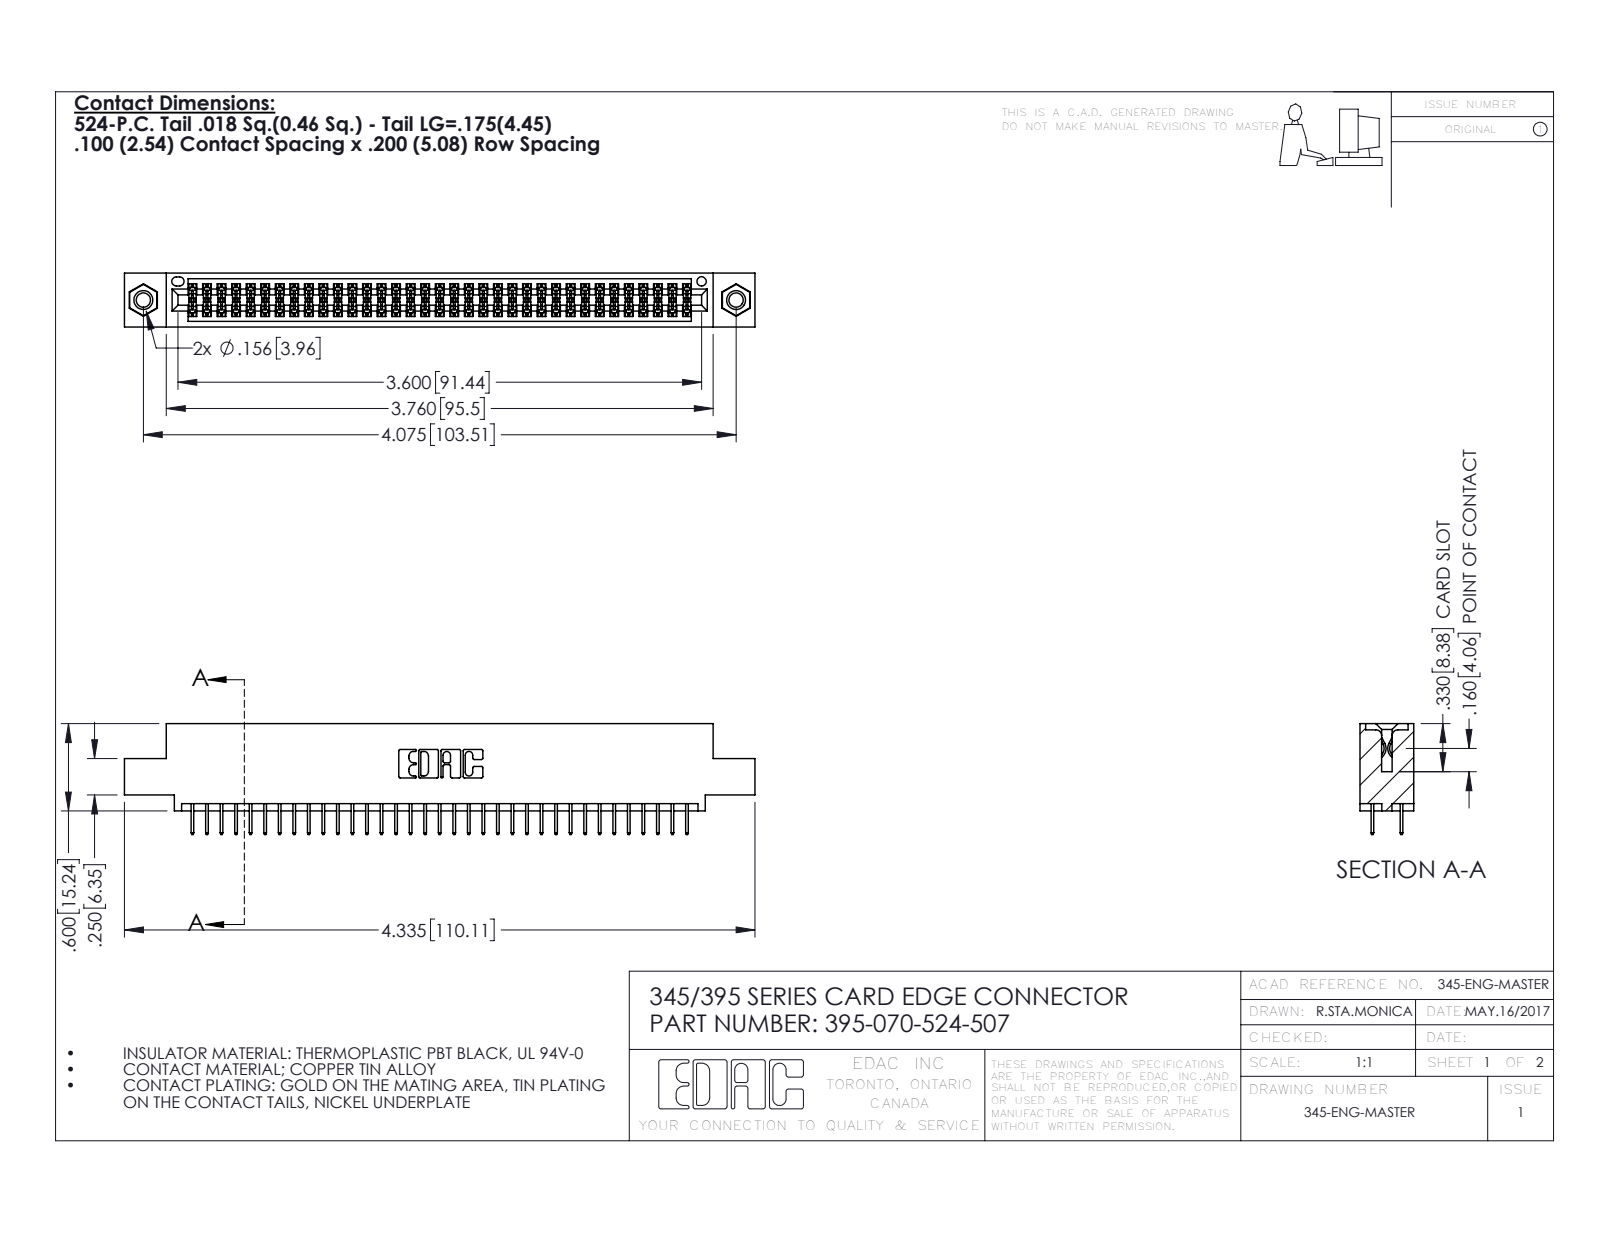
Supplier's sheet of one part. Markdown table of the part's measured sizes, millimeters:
| quantity | value |
| --- | --- |
| part name | 345 Part_0.110 Offset - 0.156 Dia-TI; 345-292-001_345-293-124; 345-250-001_345-250-005-103; 395-070-524-507 |
| STEP written by | SolidWorks 2016 (CONFIG_CONTROL_DESIGN) |
| units | millimeters |
| bodies | 73 solids, 3970 faces (2846 planar, 1108 cylindrical, 16 other) |
| overall size | 110.1 × 19.4 × 9.4 |
| volume | 10 400 mm³ |
| surface area | 15 140 mm² |
| round holes (diameter × count) | 2.5 × 2, 3.2 × 2, 4 × 2, 1.6 × 1 |
| round bosses / shafts (diameter × count) | 3.9 × 2 |
| partial cylindrical surfaces (radius × count) | 0.2 × 105, 0.3 × 22, 0.2 × 6, 0.8 × 6, 0.7 × 3, 0.4 × 2, 0.5 × 2, 0.6 × 2 |
| main face-to-face distances | 1.8, 7.6, 5.1, 9.4, 2.5, 6.9, 0.6, 5.7, 1.8, 4.4 |
| hole center spacings | 6.9, 97.5, 103.5 |
